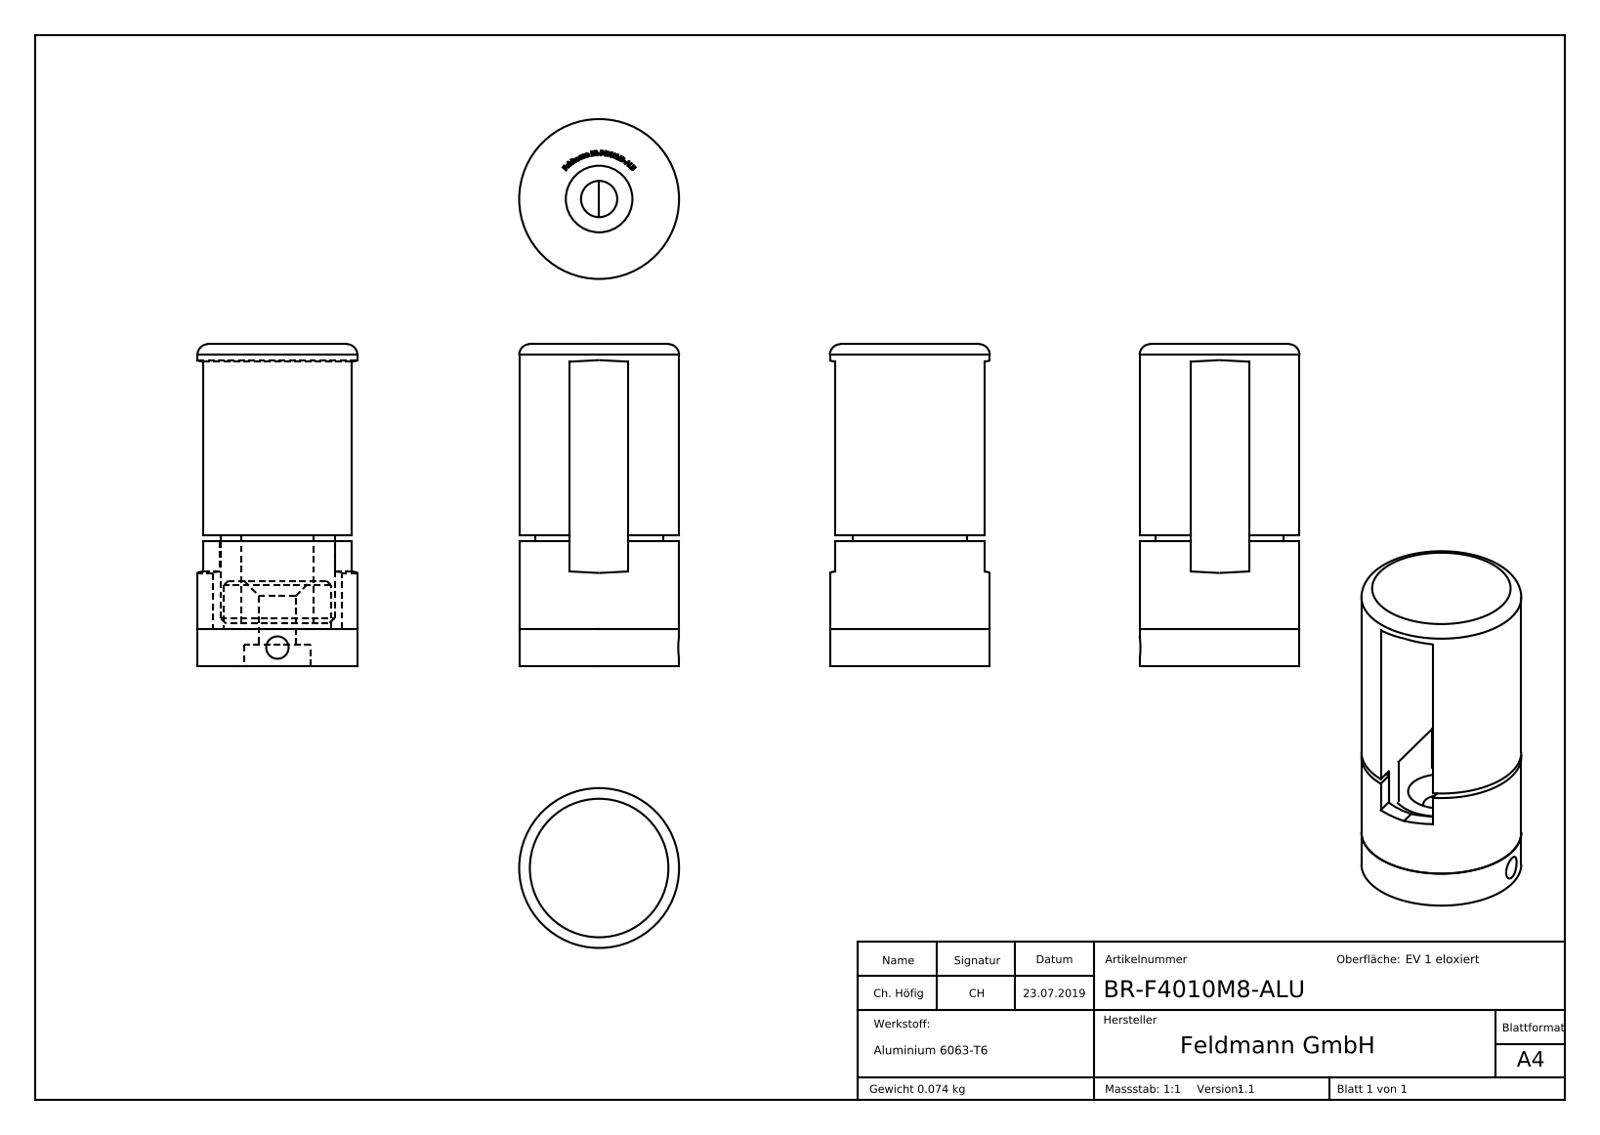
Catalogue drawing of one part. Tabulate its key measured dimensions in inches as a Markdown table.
| quantity | value |
| --- | --- |
| part name | BR-R1XM8-XXX Teil1_BR-FXXXM8-ALU Teil1; BR-R1XM8-XXX Teil2_BR-F4010M8-ALU Teil2; BR-F4010M8-ALU; BR-R1XM8-XXX Teil2 (+3 more) |
| STEP written by | SolidWorks 2015 (CONFIG_CONTROL_DESIGN) |
| units | inches |
| bodies | 3 solids, 329 faces (195 planar, 12 cylindrical, 122 other) |
| overall size | 2.533 × 1.181 × 1.181 |
| volume | 1.67 in³ |
| surface area | 20.95 in² |
| round holes (diameter × count) | 0.165 × 1, 0.268 × 1, 0.492 × 1, 0.953 × 1 |
| round bosses / shafts (diameter × count) | 1.181 × 1, 0.787 × 1 |
| partial cylindrical surfaces (radius × count) | 0.344 × 1, 0.474 × 1 |
| main face-to-face distances | 0.433, 0.276, 2.38, 2.104, 0.039, 0.652, 0.967, 0.691, 1.413, 0.927 |
